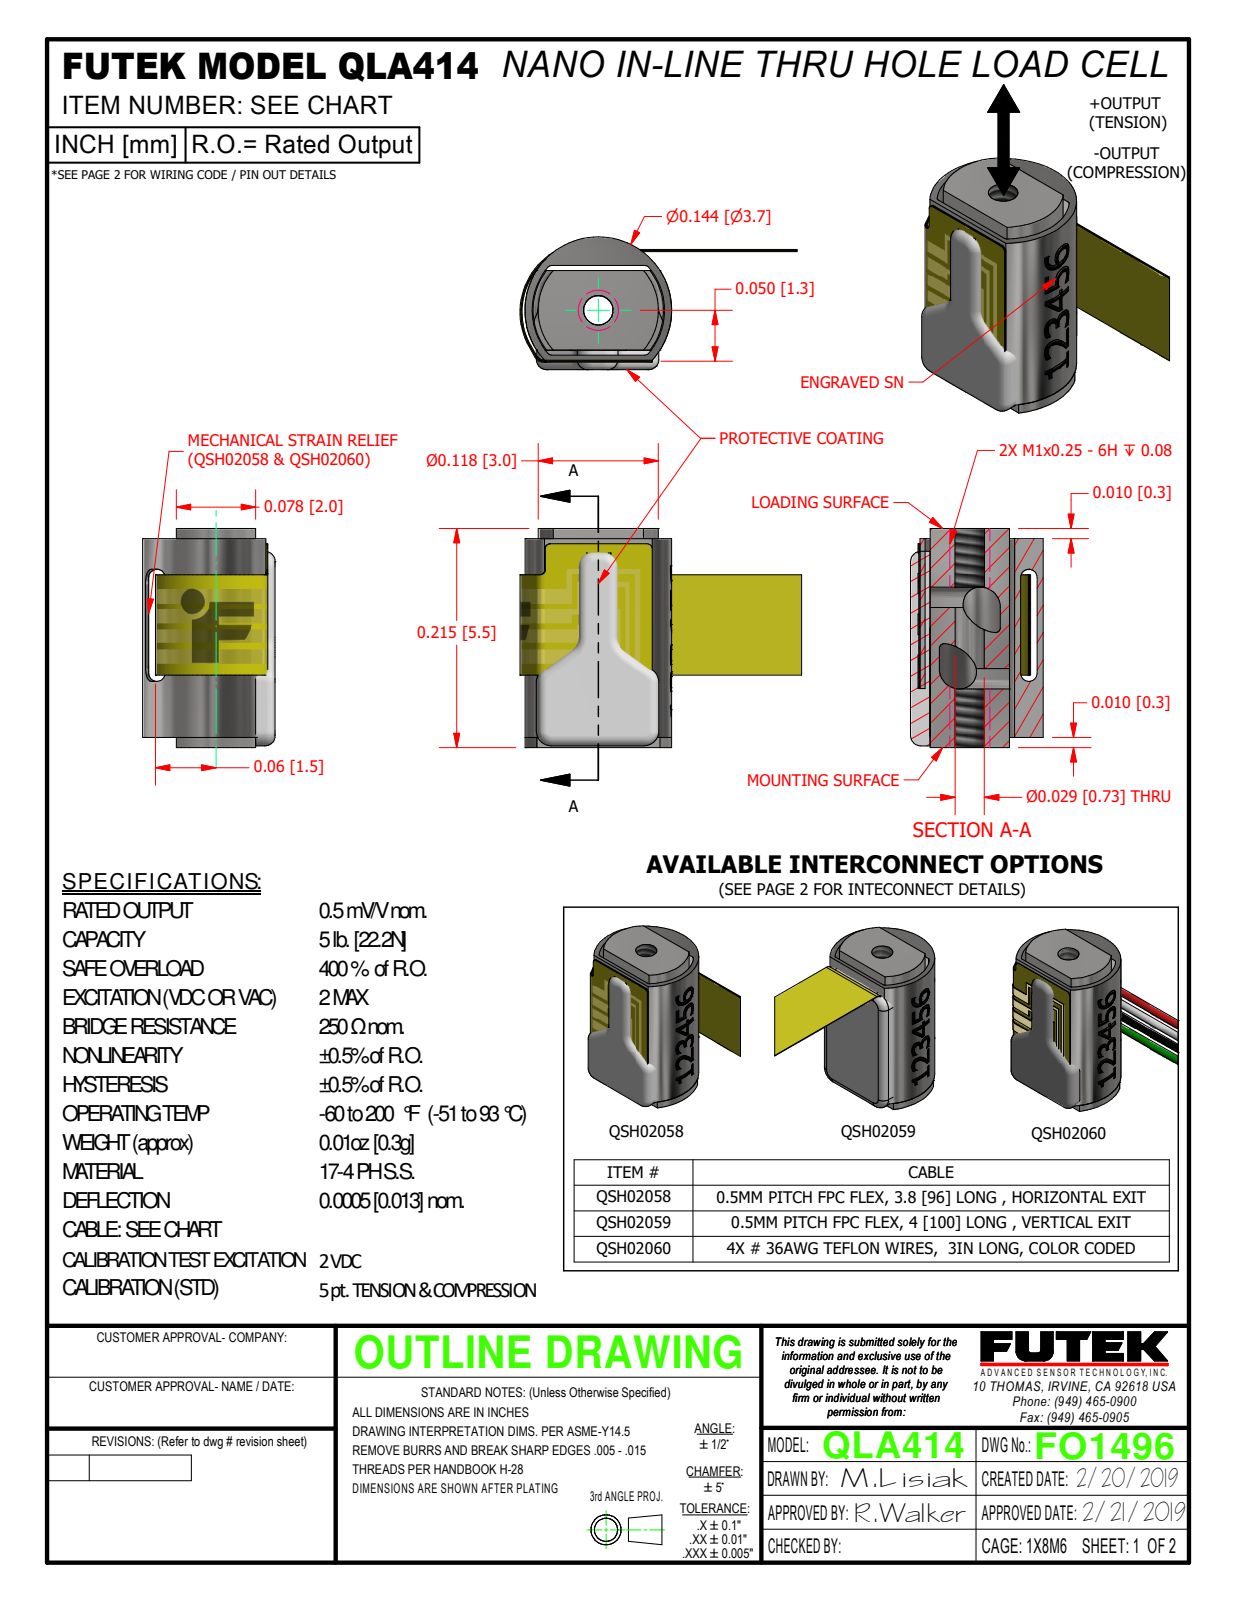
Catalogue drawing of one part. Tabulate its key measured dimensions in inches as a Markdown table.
| quantity | value |
| --- | --- |
| part name | QSH02060 |
| STEP written by | Autodesk Inventor 2020 (AUTOMOTIVE_DESIGN) |
| units | inches |
| bodies | 5 solids, 346 faces (178 planar, 81 cylindrical, 87 other) |
| overall size | 0.278 × 0.215 × 0.13 |
| volume | 0.003 in³ |
| surface area | 0.339 in² |
| round holes (diameter × count) | 0.029 × 1, 0.029 × 1 |
| round bosses / shafts (diameter × count) | 0.01 × 4 |
| partial cylindrical surfaces (radius × count) | 0.015 × 12, 0.01 × 9, 0.005 × 7, 0.008 × 4, 0.017 × 2, 0.04 × 2, 0.011 × 1, 0.011 × 1 |
| main face-to-face distances | 0.083, 0.089, 0.094, 0.097, 0.108, 0.102, 0.019, 0.078, 0.215, 0.014 |
